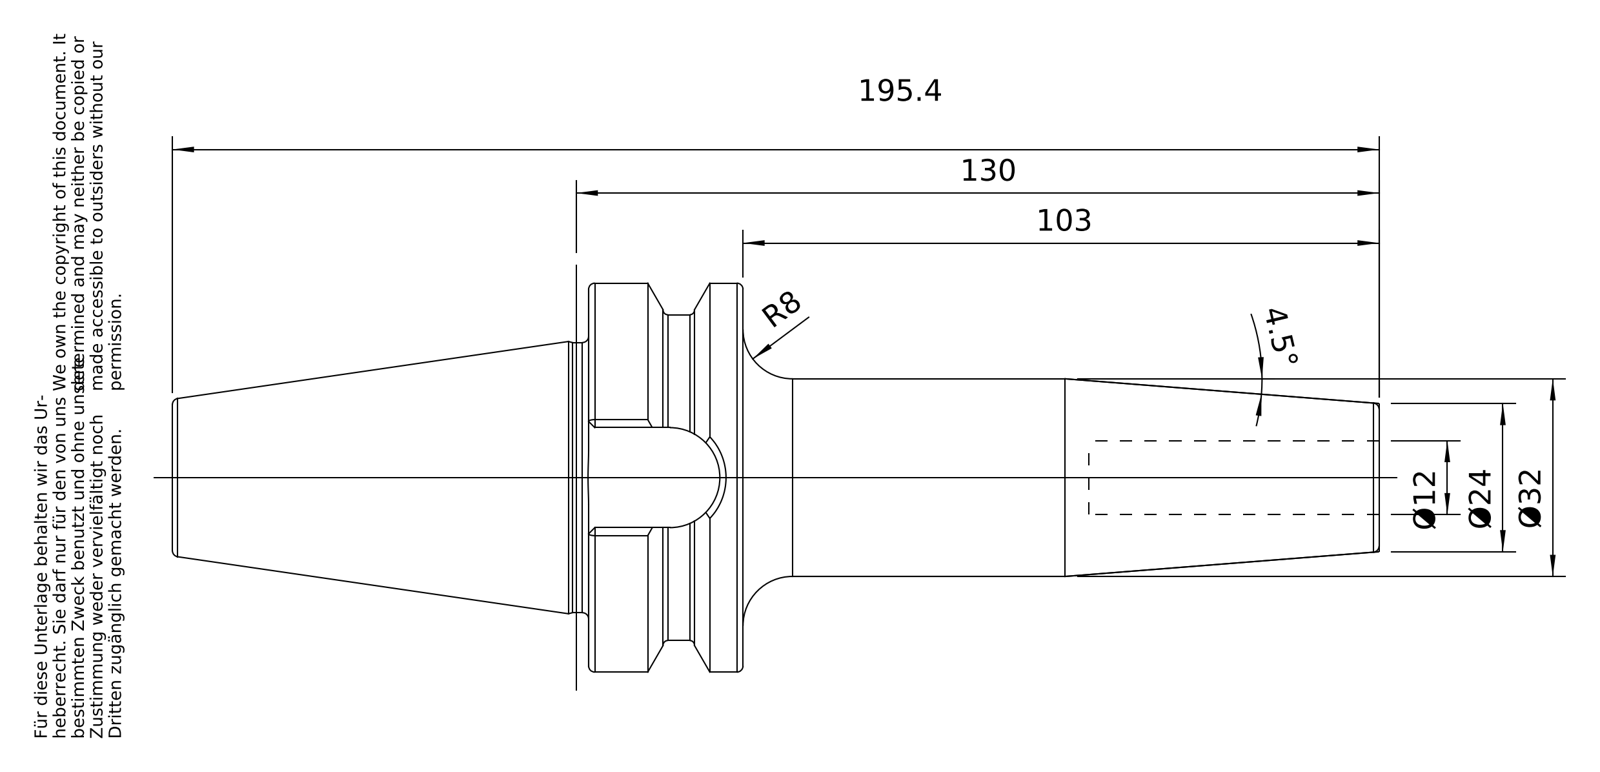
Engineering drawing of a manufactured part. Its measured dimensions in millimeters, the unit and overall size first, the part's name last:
Units: millimetres
Overall size (bounding box): 195.4 × 62.98 × 62.98
Round holes (diameter × count): ⌀12 ×1, ⌀13.84 ×1, ⌀17.01 ×1, ⌀17.5 ×1
Round bosses / shafts (diameter × count): ⌀62.98 ×1, ⌀52.75 ×1, ⌀43.75 ×1, ⌀32 ×1, ⌀16.01 ×1
Partial cylindrical surfaces — rounded edges, fillets, slot ends (radius × count): R8.1 ×1
Main face-to-face distances: 25, 44.9, 128, 103, 16.2, 67.4, 92.4, 195.4, 148.4, 81
Volume: 195 818 mm³ · Surface area: 32 639 mm²
Bodies: 1 solid, 96 faces (26 planar, 22 cylindrical, 48 other)
Part name (STEP PRODUCT): 40-644-12
STEP written by: PRO/ENGINEER BY PARAMETRIC TECHNOLOGY CORPORATION, 2010430 (CONFIG_CONTROL_DESIGN)
